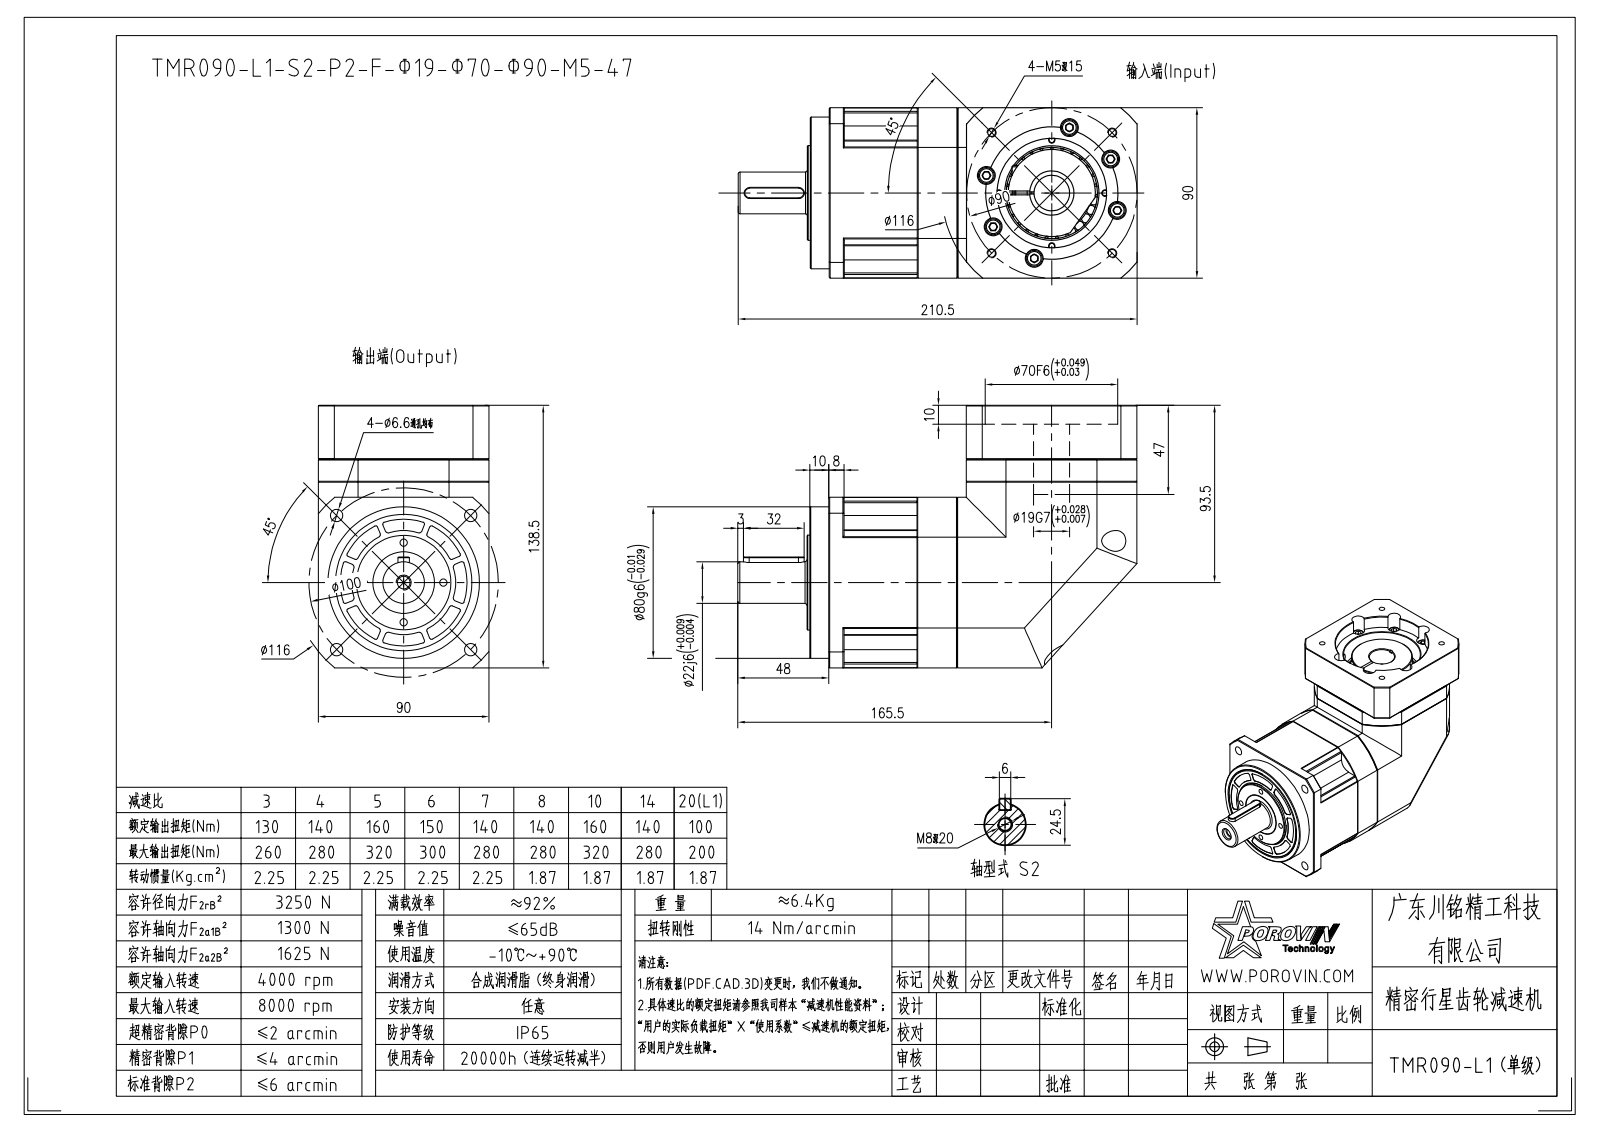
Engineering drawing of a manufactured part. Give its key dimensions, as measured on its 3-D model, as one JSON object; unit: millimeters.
{"part_name": "HEXAGON_SOCKET_HEAD_CAP_S-13622; SPRING_LOCK_WASHERS--NORM-24193; SPRING_LOCK_WASHERS--NORMA-2869; HEXAGON_SOCKET_HEAD_CAP_SC-2921 (+8 more)", "step_written_by": "CREO PARAMETRIC BY PTC INC, 2020053 (CONFIG_CONTROL_DESIGN)", "units": "millimeters", "bodies": {"solids": 42, "faces": 1283, "planar": 512, "cylindrical": 545, "other": 226}, "overall_size": [210.5, 138.5, 90], "volume_mm3": 1341000, "surface_area_mm2": 207984, "round_holes": [[5.4, 12], [5.5, 12], [9.5, 12], [4.2, 11], [6.5, 5], [4, 4], [6.6, 4], [6.68, 4], [11, 4], [5, 1], [6.8, 1], [8.4, 1]], "round_bosses_or_shafts": [[8.5, 12], [8, 12], [5, 12], [10, 4], [9.88, 4], [6, 4], [80, 1], [78, 1]], "partial_cylinders_radius": [[1, 92], [7.5, 4], [51, 3], [3, 2], [58, 2], [4, 1], [5.25, 1], [20.75, 1]], "face_to_face_distances": [90, 12, 21.3, 21.5, 10, 26, 110, 28.5, 98, 31.3], "hole_center_spacings": [35.75, 27.36, 38.16, 66.06, 66.53, 64.31, 80.07, 13.97]}
